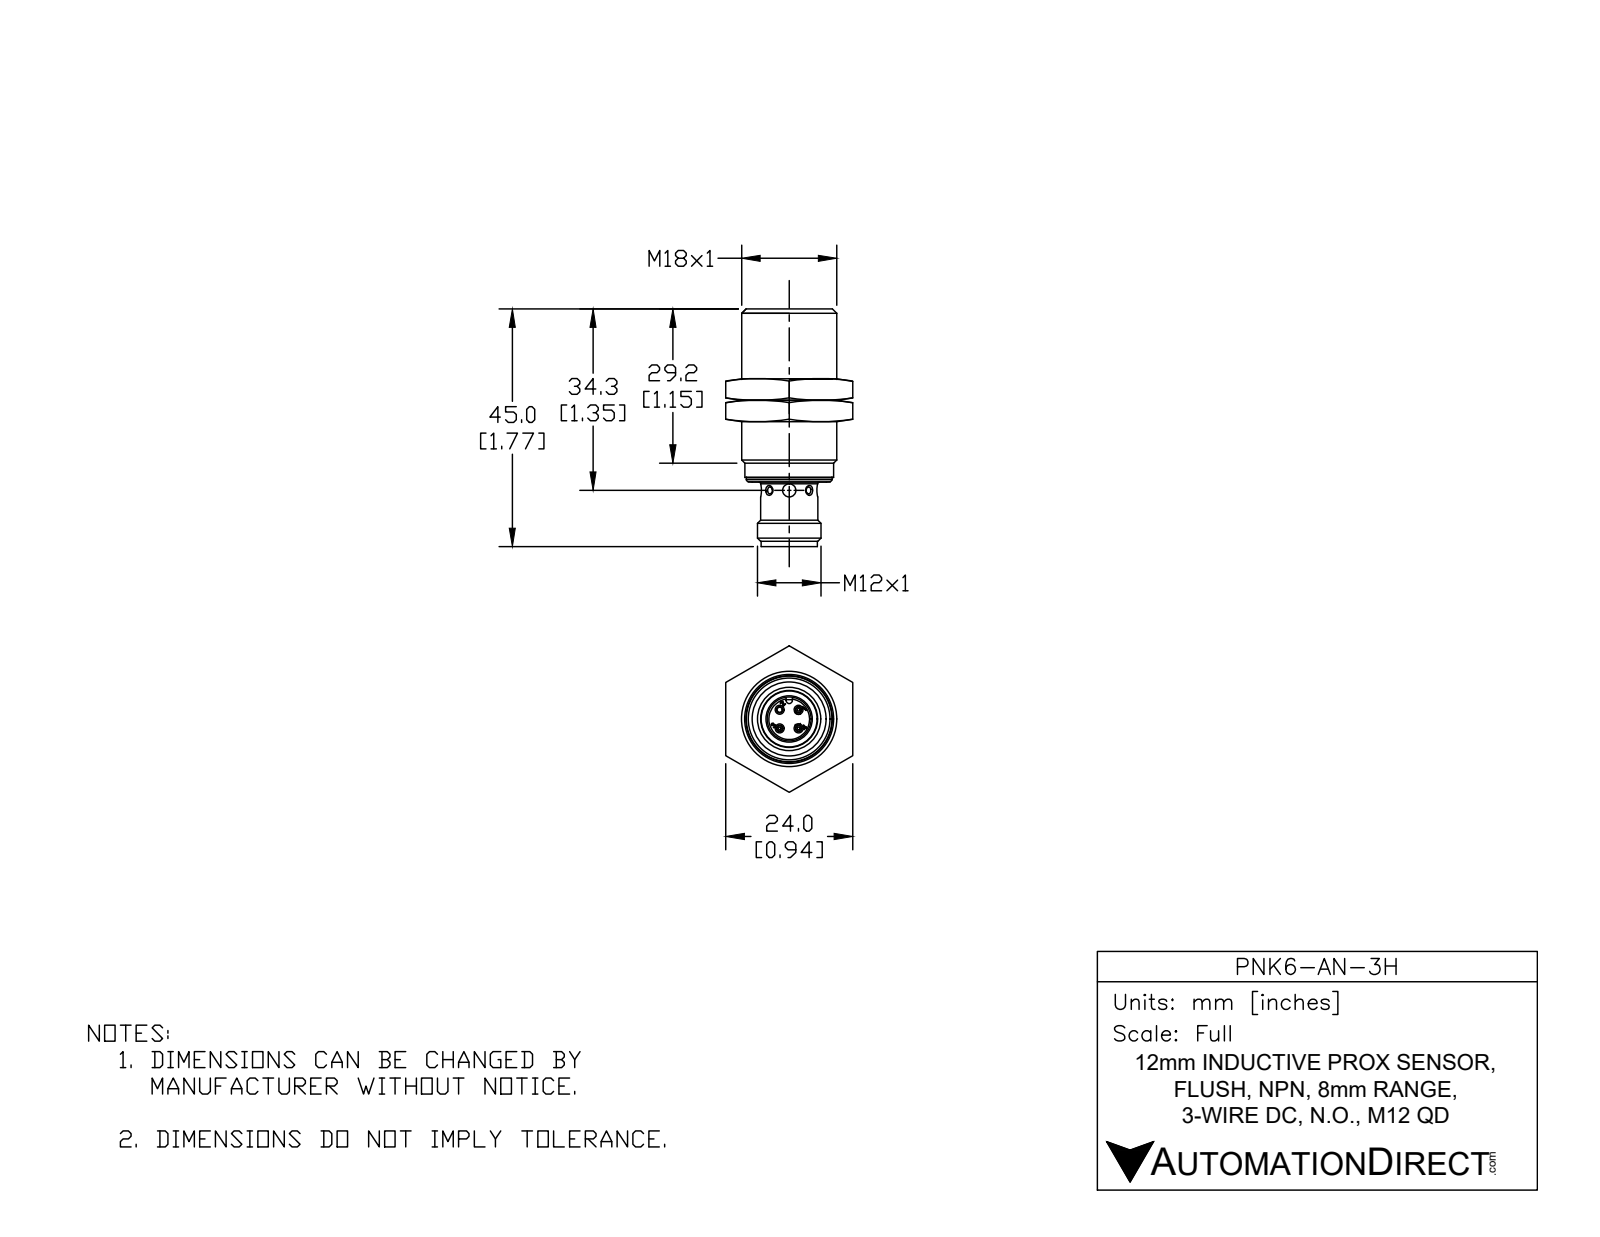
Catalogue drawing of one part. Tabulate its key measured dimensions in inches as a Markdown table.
| quantity | value |
| --- | --- |
| part name | PNK6-AN-3H |
| STEP written by | SolidWorks 2017 (AUTOMOTIVE_DESIGN) |
| units | inches |
| bodies | 1 solid, 476 faces (118 planar, 129 cylindrical, 229 other) |
| overall size | 1.772 × 0.709 × 0.709 |
| volume | 0.401 in³ |
| surface area | 7.642 in² |
| round holes (diameter × count) | 0.04 × 3, 0.043 × 3, 0.098 × 2, 0.038 × 1, 0.323 × 1, 0.327 × 1, 0.394 × 1, 0.618 × 1 |
| round bosses / shafts (diameter × count) | 0.039 × 9, 0.709 × 1, 0.661 × 1, 0.642 × 1, 0.638 × 1, 0.616 × 1, 0.472 × 1, 0.425 × 1 |
| partial cylindrical surfaces (radius × count) | 0.004 × 24, 0.039 × 6, 0.071 × 6, 0.024 × 1, 0.031 × 1 |
| main face-to-face distances | 0.452, 0.03, 0.422, 1.236, 1.207, 0.785, 1.291, 0.055, 1.262, 0.84 |
| hole center spacings | 0.098, 0.139, 0.197 |
